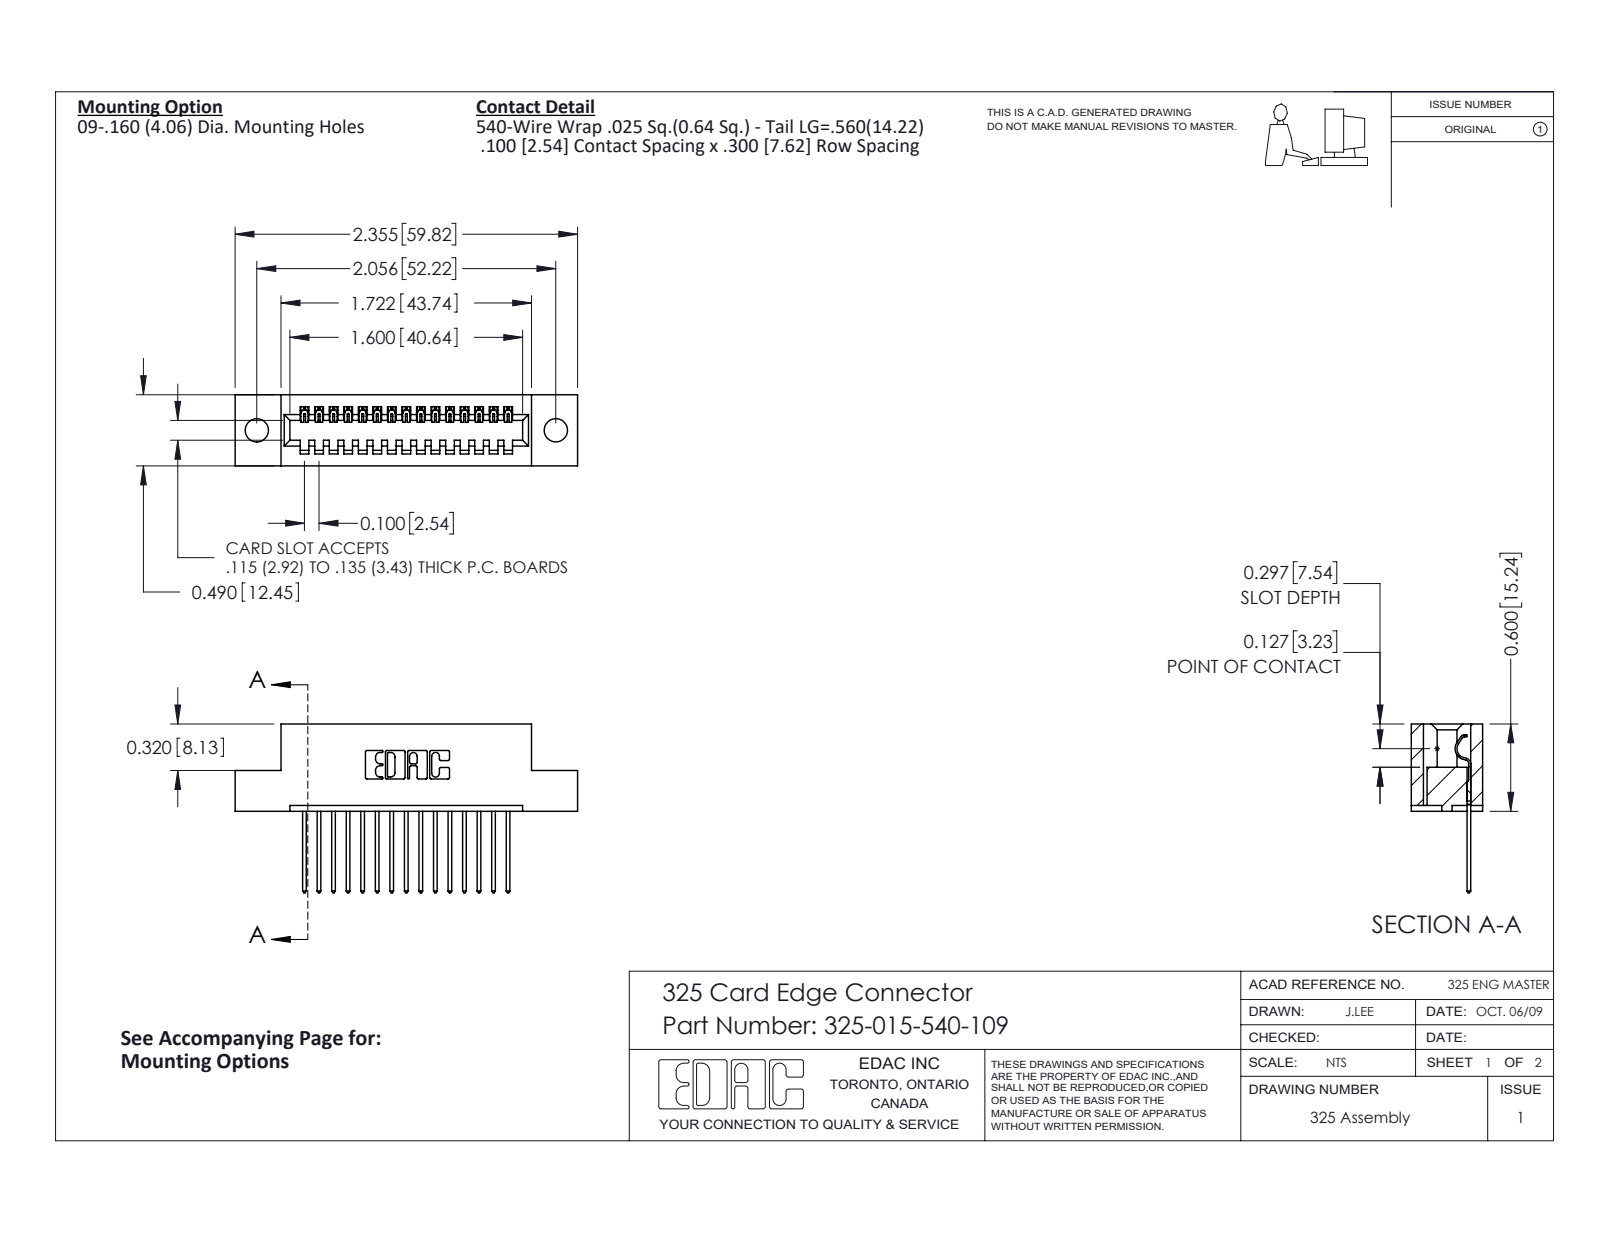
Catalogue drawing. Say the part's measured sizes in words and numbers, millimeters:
The part is named "325-292-001_325-293-140; 325 Part_.160 TH; 325-015-540-109". Its 3-D file was written by "SolidWorks 2016 (CONFIG_CONTROL_DESIGN)". It is 16 solids with 984 faces: 700 planar, 284 cylindrical and 0 other. Overall it measures 59.8 by 29.5 by 12.4 millimeters. Its volume is 7 180 cubic millimeters and its surface area 7 419 square millimeters. Round holes: 2 of diameter 4.1. Partial cylindrical surfaces (rounded edges, fillets, slot ends): 30 of radius 0.2, 30 of radius 0.3, 22 of radius 0.3, 6 of radius 0.2, 6 of radius 0.8, 3 of radius 0.7, 1 of radius 0.4, 1 of radius 0.6. The main face-to-face distances are 2.1, 10.3, 7.6, 12.4, 2.7, 9.7, 0.6, 1, 2.5, 15.2. The hole center spacings are 52.2.
